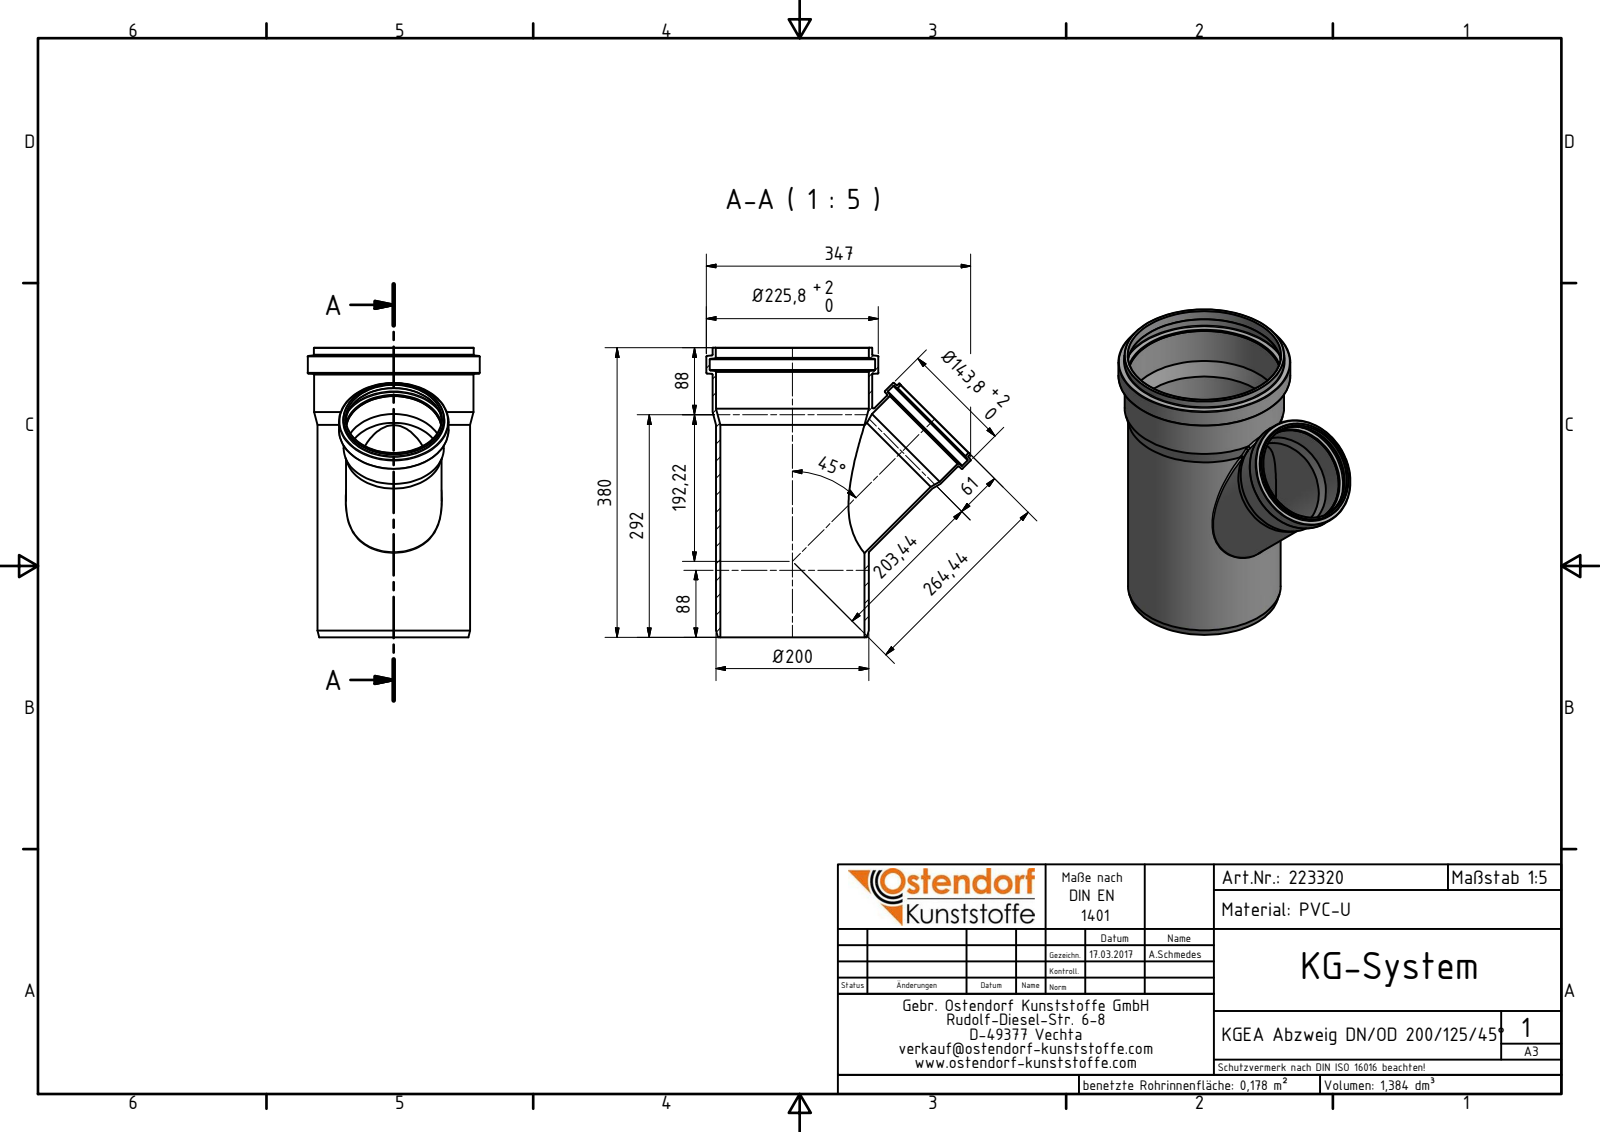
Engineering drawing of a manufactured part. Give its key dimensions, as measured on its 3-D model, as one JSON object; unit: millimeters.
{"part_name": "223320 KGEA Abzweig DN_OD 200_125_45°", "step_written_by": "Autodesk Inventor 2016 (AUTOMOTIVE_DESIGN)", "units": "millimeters", "bodies": {"solids": 1, "faces": 64, "planar": 5, "cylindrical": 18, "other": 41}, "overall_size": [380, 347, 225.8], "volume_mm3": 1384000, "surface_area_mm2": 581493, "round_holes": [[126, 2], [118.8, 1], [125.7, 1], [138, 1], [189.3, 1], [200.6, 1], [200.9, 1], [217, 1]], "round_bosses_or_shafts": [[225.8, 1], [209.7, 1], [209.4, 1], [200.5, 1], [143.8, 1], [131.8, 1], [131.5, 1], [125.2, 1]], "face_to_face_distances": [380, 348.23, 31.77, 20.67]}
